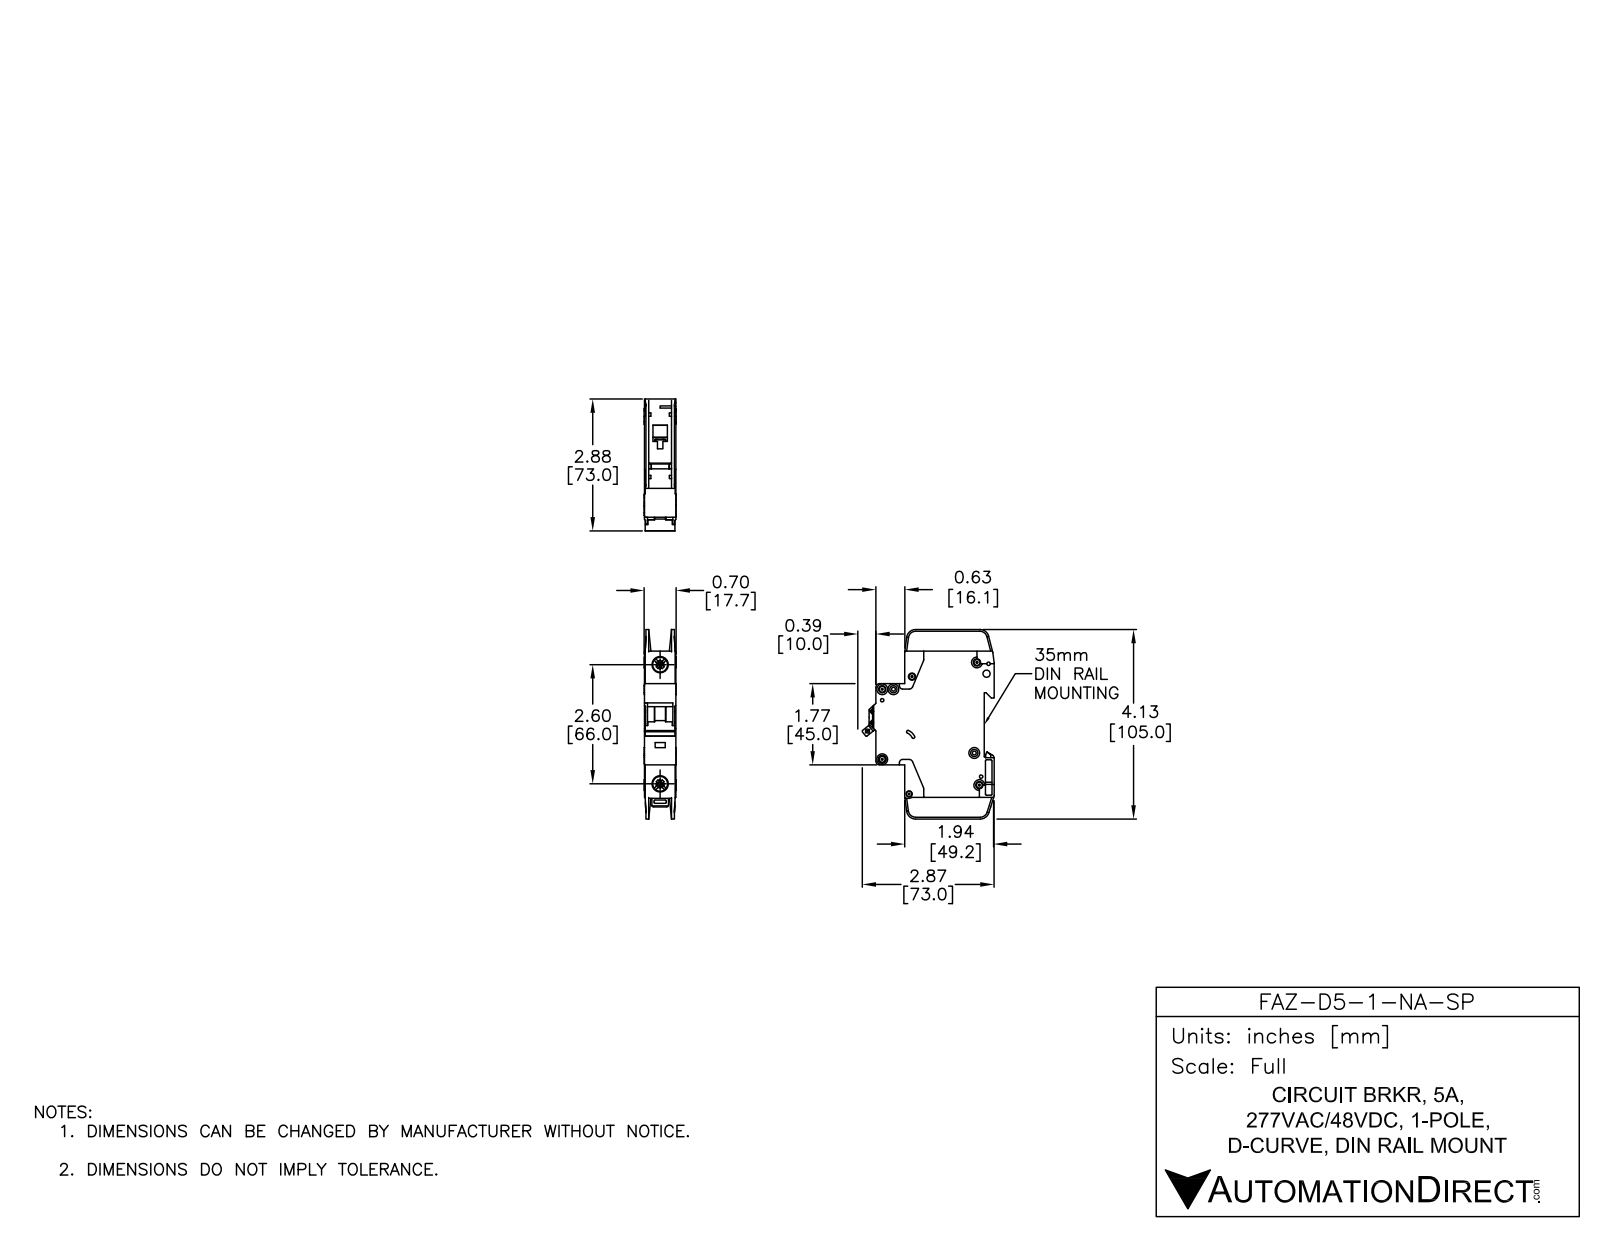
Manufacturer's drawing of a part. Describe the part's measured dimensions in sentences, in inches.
The part is named "FAZ-D5-1-NA-SP". Its 3-D file was written by "SolidWorks 2014 (AUTOMOTIVE_DESIGN)". It is 3 solids with 784 faces: 409 planar, 263 cylindrical and 112 other. Overall it measures 4.134 by 2.876 by 0.697 inches. Its volume is 4.741 cubic inches and its surface area 38.35 square inches. Round holes: 7 of diameter 0.142, 2 of diameter 0.043, 2 of diameter 0.059, 2 of diameter 0.157, 2 of diameter 0.281, 2 of diameter 0.323, 1 of diameter 0.075, 1 of diameter 0.085, 1 of diameter 0.087, 1 of diameter 0.1, 1 of diameter 0.13, 1 of diameter 0.134. Round bosses or shafts: 7 of diameter 0.236, 1 of diameter 0.098. Partial cylindrical surfaces (rounded edges, fillets, slot ends): 29 of radius 0.01, 18 of radius 0.02, 10 of radius 0.039, 10 of radius 0.079, 5 of radius 0.197, 4 of radius 0.157, 3 of radius 0.071, 2 of radius 0.008. The main face-to-face distances are 0.689, 0.593, 0.028, 0.096, 0.069, 0.62, 0.524, 0.551, 0.496, 0.079. The hole center spacings are 0.244, 0.204, 0.24, 0.322, 0.337, 0.343, 0.437, 0.49.
